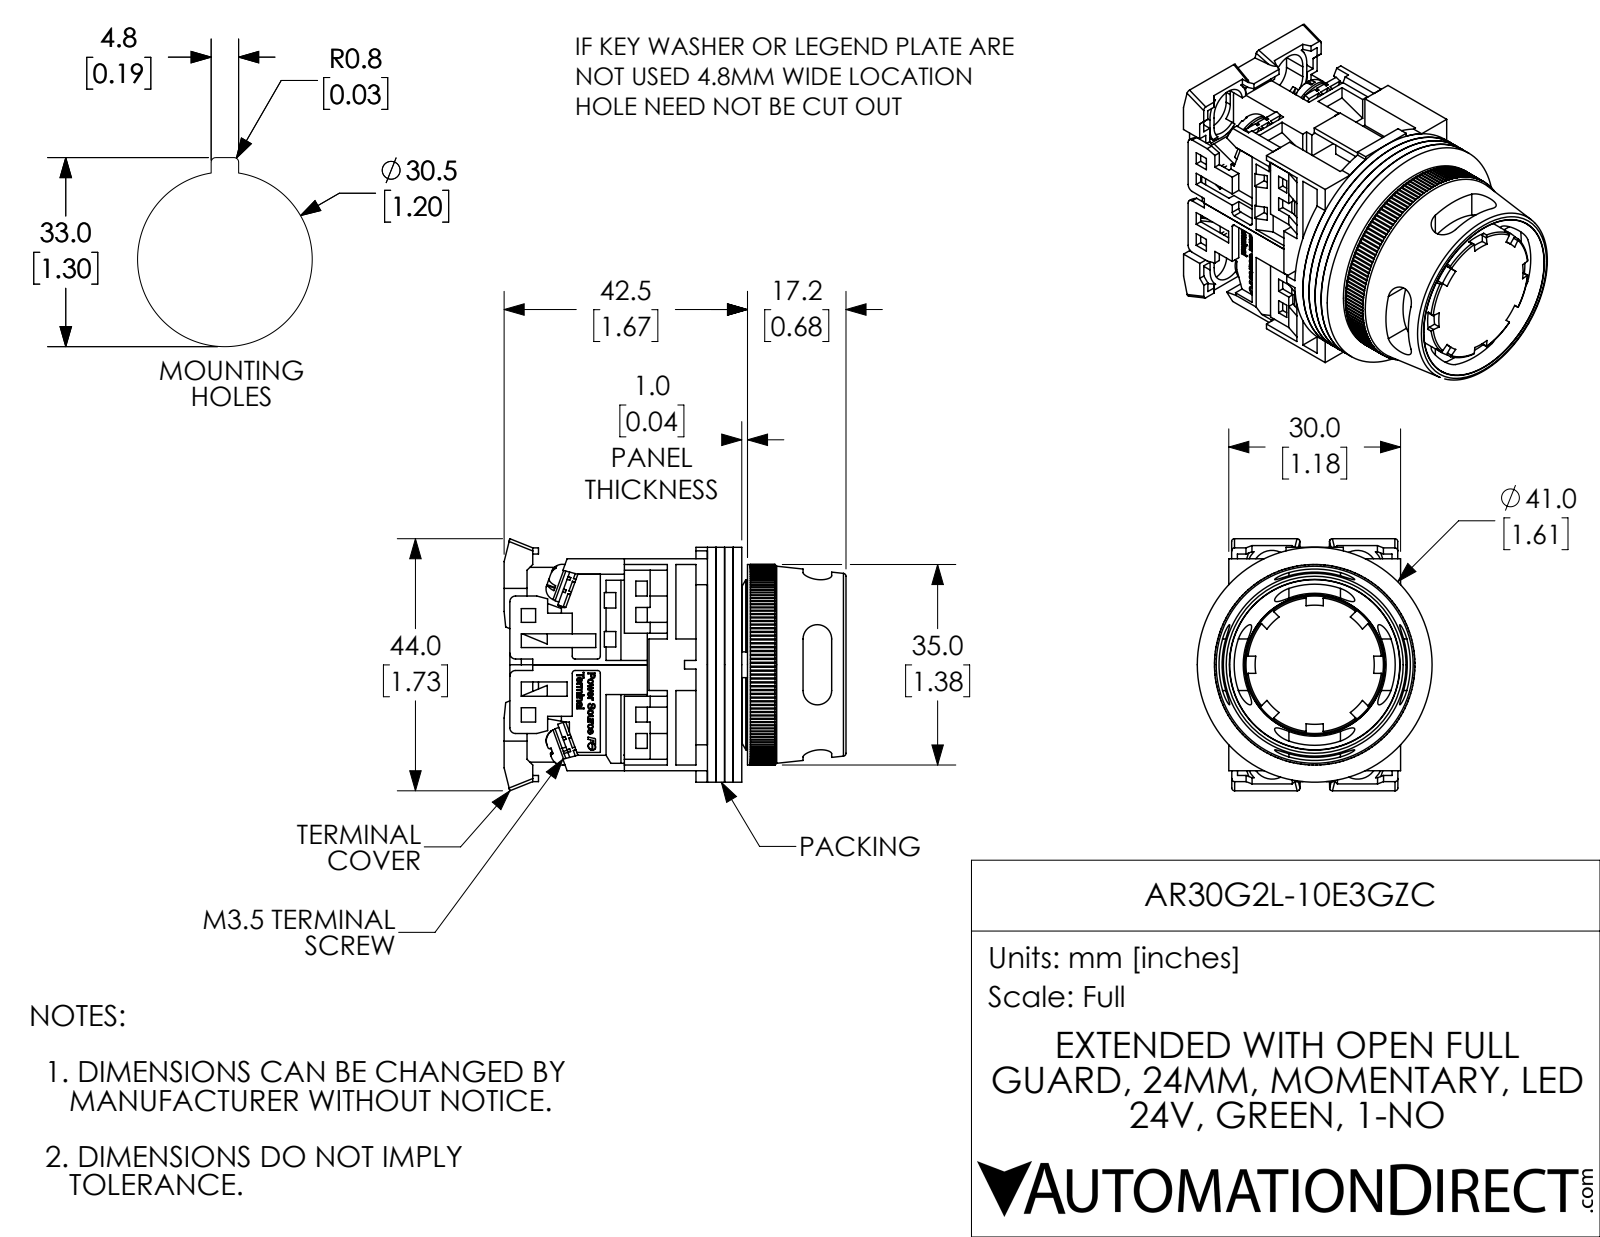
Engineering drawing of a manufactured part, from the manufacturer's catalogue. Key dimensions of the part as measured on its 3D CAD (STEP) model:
Part name (STEP PRODUCT): AR30G2L-10E3GZC
STEP written by: SolidWorks 2017 (AUTOMOTIVE_DESIGN)
Units: inches
Bodies: 25 solids, 2179 faces (1508 planar, 458 cylindrical, 213 other)
Overall size (bounding box): 2.35 × 1.732 × 1.614
Volume: 2.142 in³ · Surface area: 62.62 in²
Round holes (diameter × count): ⌀0.138 ×8, ⌀0.142 ×4, ⌀0.118 ×1, ⌀0.472 ×1, ⌀0.709 ×1, ⌀0.728 ×1, ⌀0.787 ×1, ⌀0.945 ×1, ⌀1.252 ×1
Round bosses / shafts (diameter × count): ⌀0.26 ×4, ⌀0.138 ×4, ⌀1.614 ×1, ⌀1.378 ×1, ⌀1.181 ×1, ⌀0.866 ×1, ⌀0.776 ×1, ⌀0.551 ×1
Partial cylindrical surfaces — rounded edges, fillets, slot ends (radius × count): R0.01 ×160, R0.012 ×16, R0.059 ×16, R0.02 ×12, R0.039 ×4, R0.098 ×4, R0.138 ×4, R0.177 ×4
Main face-to-face distances: 0.059, 0.118, 0.039, 0.177, 0.276, 1.417, 0.728, 0.811, 0.079, 1.358
Hole centre spacings: 0.579, 0.61
